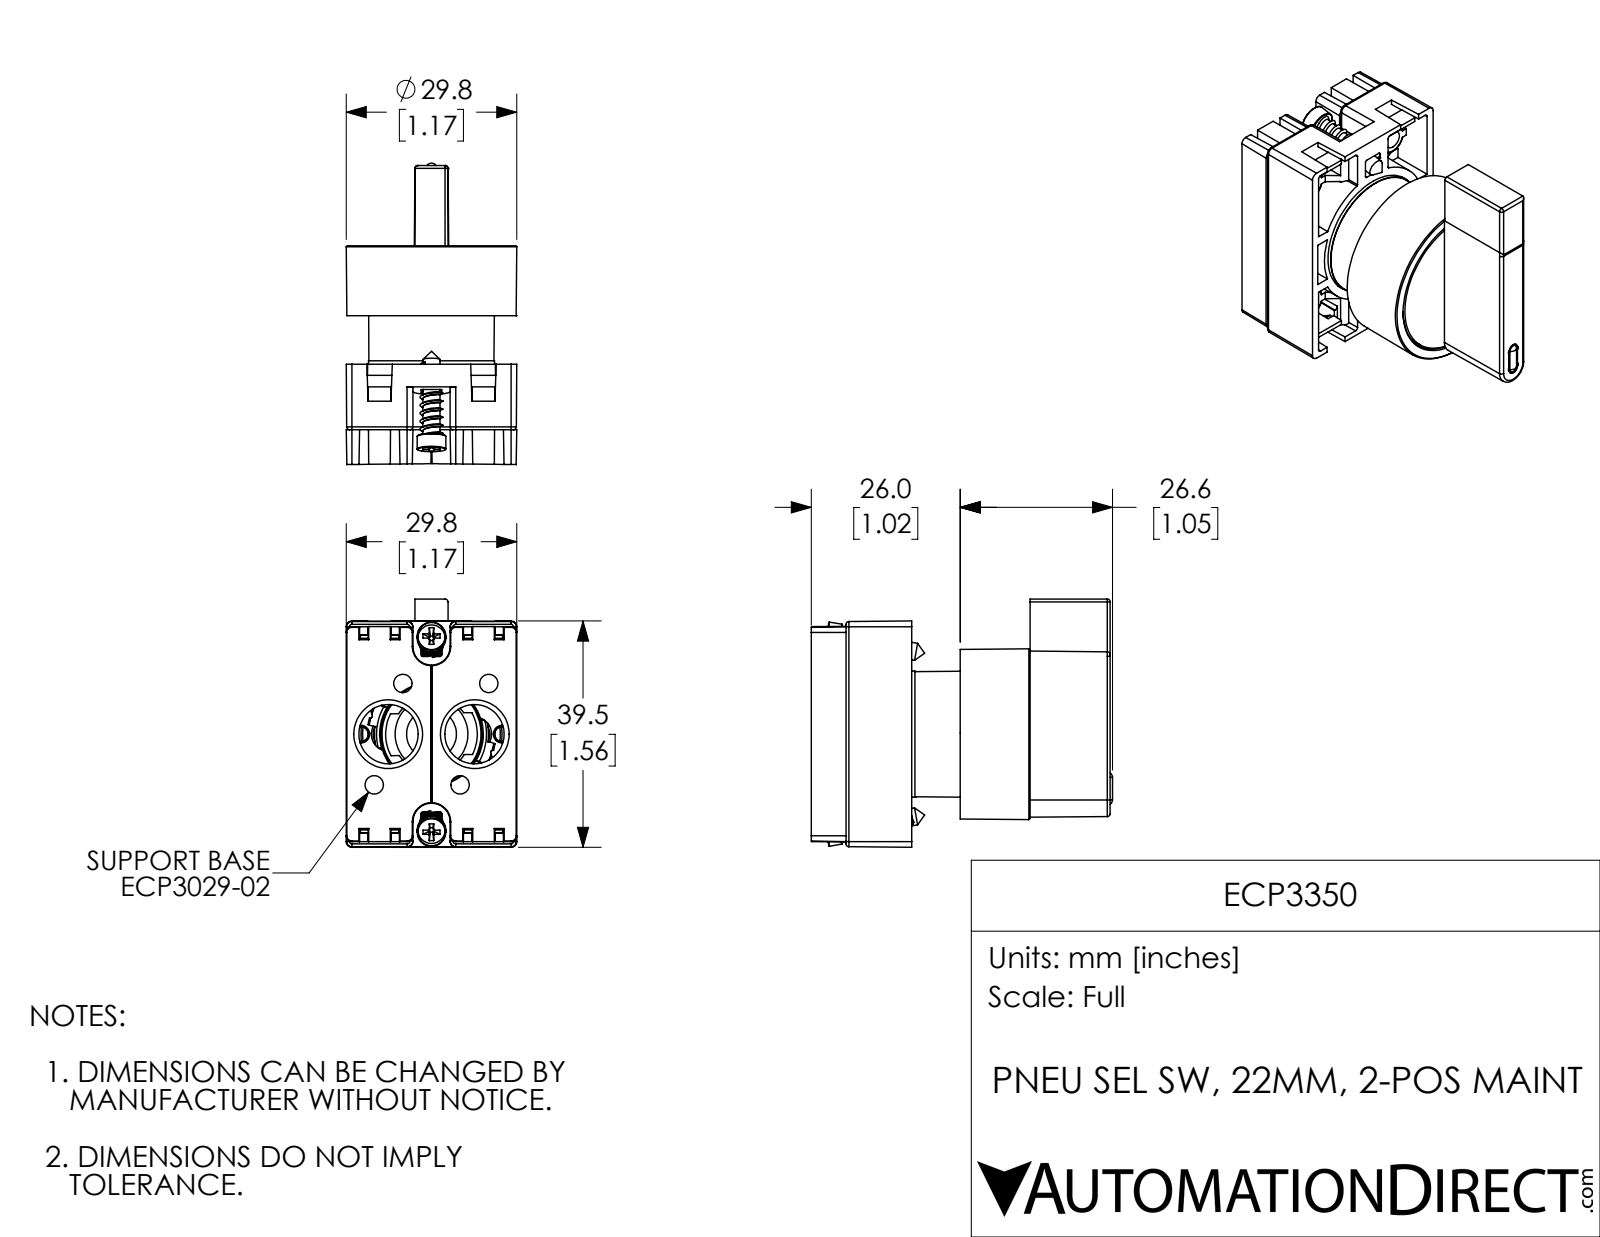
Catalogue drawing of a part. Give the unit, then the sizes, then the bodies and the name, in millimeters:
Units: millimetres
Overall size (bounding box): 52.6 × 43.3 × 29.8
Round holes (diameter × count): ⌀2.1 ×4, ⌀10.3 ×2, ⌀12.7 ×1, ⌀14 ×1, ⌀17.7 ×1, ⌀19.1 ×1, ⌀19.2 ×1, ⌀21.7 ×1, ⌀24.8 ×1, ⌀26 ×1
Round bosses / shafts (diameter × count): ⌀5 ×2, ⌀3 ×2, ⌀25.5 ×1, ⌀22 ×1, ⌀21.6 ×1, ⌀17 ×1, ⌀8.7 ×1
Partial cylindrical surfaces — rounded edges, fillets, slot ends (radius × count): R0.5 ×23, R0.3 ×10, R1 ×9, R0.2 ×8, R0.2 ×4, R0.2 ×2, R3 ×2, R3.3 ×2
Main face-to-face distances: 32.1, 1.5, 1.7, 18.1, 18.9, 7.6, 18.1, 18.2, 20.7, 11.5
Hole centre spacings: 7.7, 13.7, 20.8, 7.5, 12, 24.7, 27.5, 15
Volume: 18 750 mm³ · Surface area: 20 890 mm²
Bodies: 9 solids, 850 faces (410 planar, 161 cylindrical, 279 other)
Part name (STEP PRODUCT): ECP3350
STEP written by: SolidWorks 2017 (AUTOMOTIVE_DESIGN)
